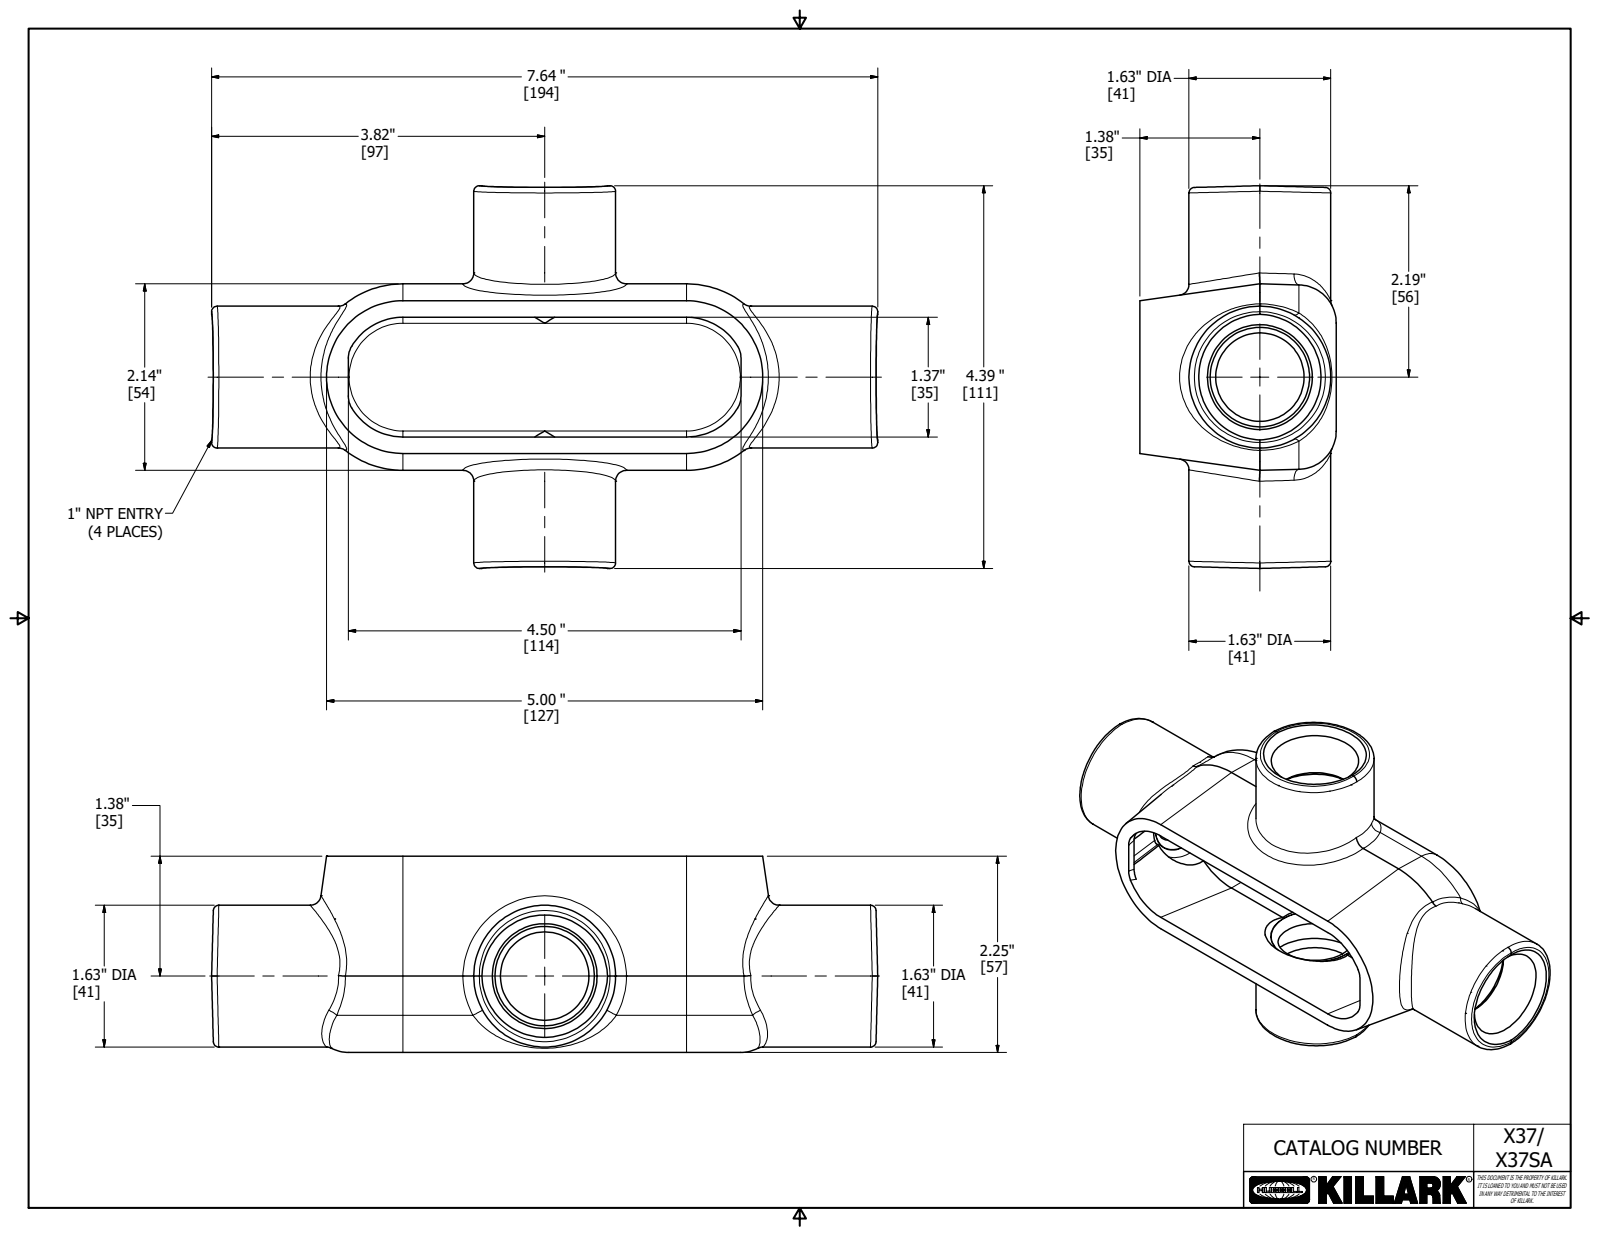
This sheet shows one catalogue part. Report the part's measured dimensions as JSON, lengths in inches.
{"part_name": "17676", "step_written_by": "Autodesk Inventor 2018 (AUTOMOTIVE_DESIGN)", "units": "inches", "bodies": {"solids": 1, "faces": 146, "planar": 46, "cylindrical": 28, "other": 72}, "overall_size": [7.635, 4.385, 2.25], "volume_in3": 9.862, "surface_area_in2": 108.3, "round_holes": [[1.321, 2], [1.375, 1], [1.375, 1]], "round_bosses_or_shafts": [[1.625, 2]], "partial_cylinders_radius": [[0.05, 4], [0.125, 4], [0.25, 2], [0.437, 2], [0.687, 1]], "face_to_face_distances": [0.187, 2.25, 2.062, 0.189, 0.031, 0.156, 2.219, 3.261, 3.072, 1.125]}
